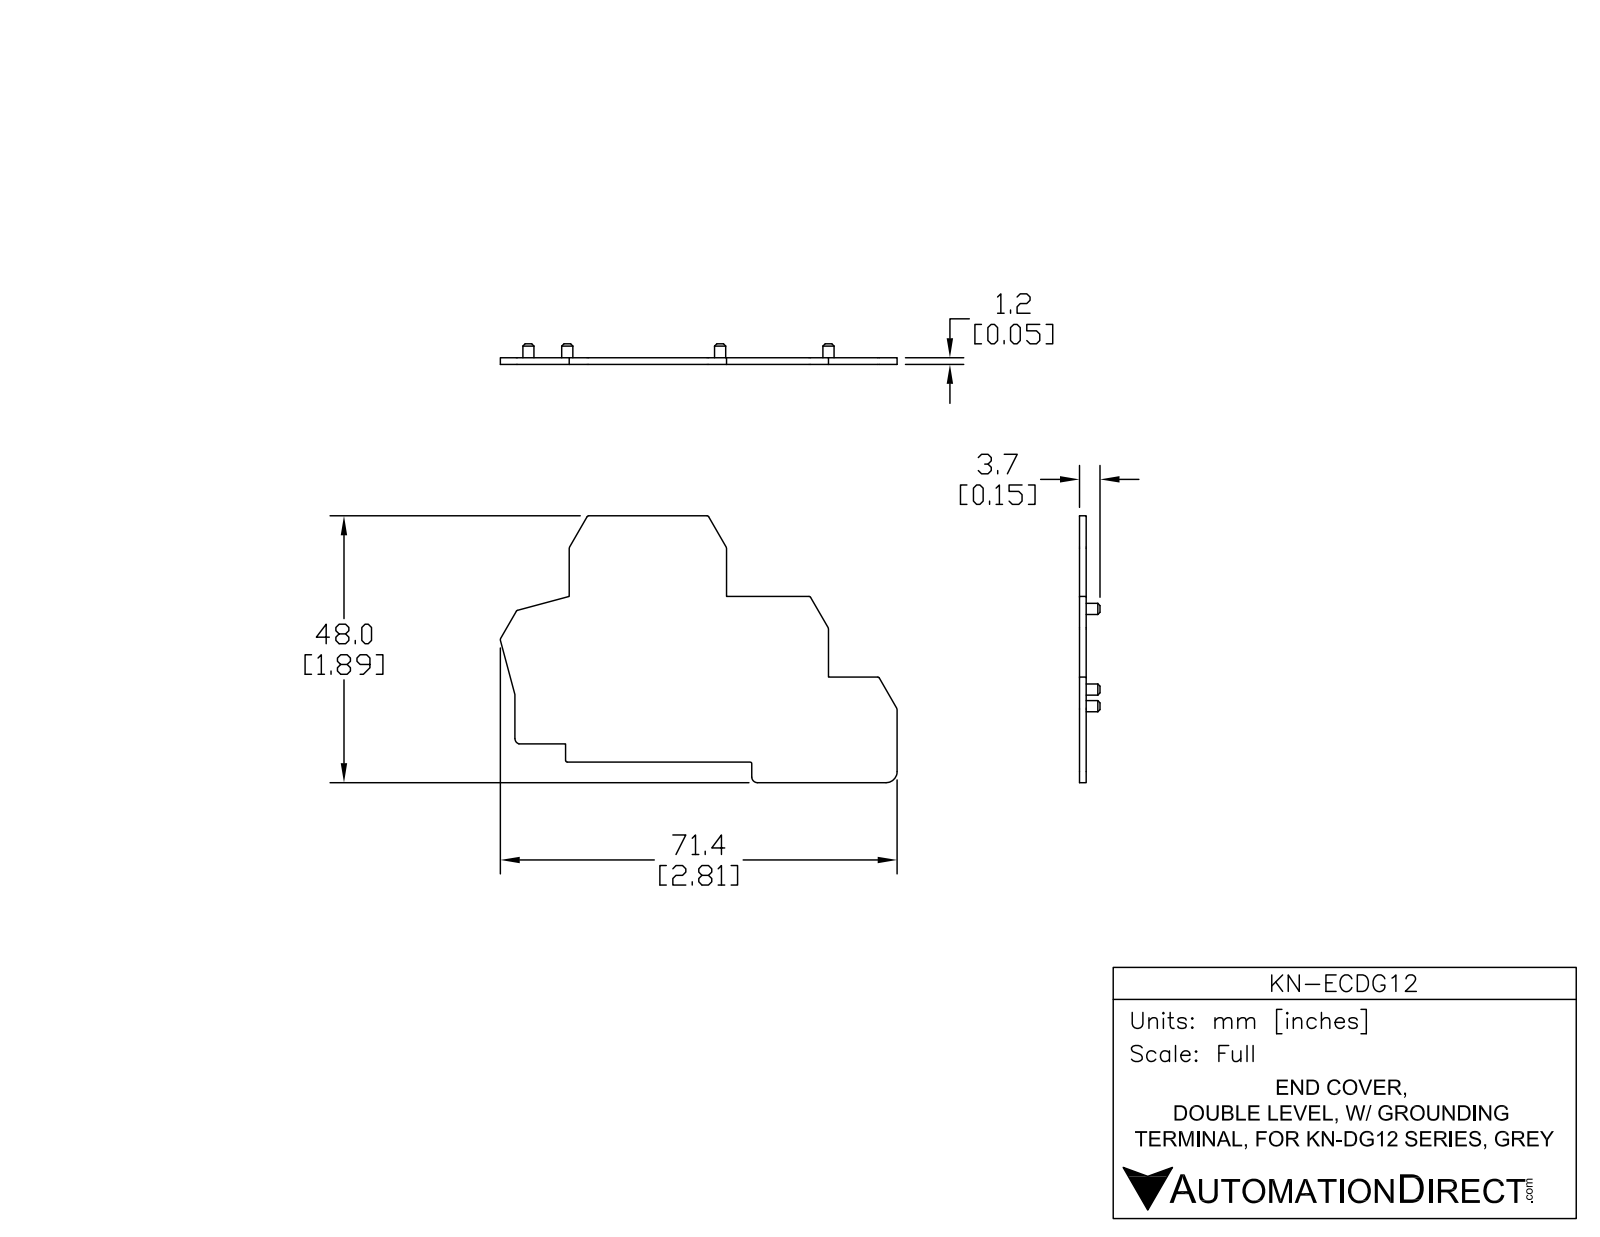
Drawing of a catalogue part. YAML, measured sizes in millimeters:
part_name: "KN-ECDG12"
step_written_by: "SolidWorks 2014 (AUTOMOTIVE_DESIGN)"
units: millimeters
bodies: {solids: 1, faces: 67, planar: 27, cylindrical: 32, other: 8}
overall_size: [71.4, 48, 3.7]
volume: 2796
surface_area: 4987
round_holes:
  - {diameter: 1.2, count: 4}
round_bosses_or_shafts:
  - {diameter: 2, count: 4}
partial_cylinders:
  - {radius: 0.3, count: 9}
  - {radius: 0.5, count: 4}
  - {radius: 1, count: 2}
  - {radius: 2, count: 1}
face_to_face_distances: [1.2, 14.5, 3.7, 48, 44.3, 33.5, 29.8, 19, 15.3, 29]
hole_center_spacings: [18.85, 24.3, 27.5, 38.68, 49.19, 54.08]
